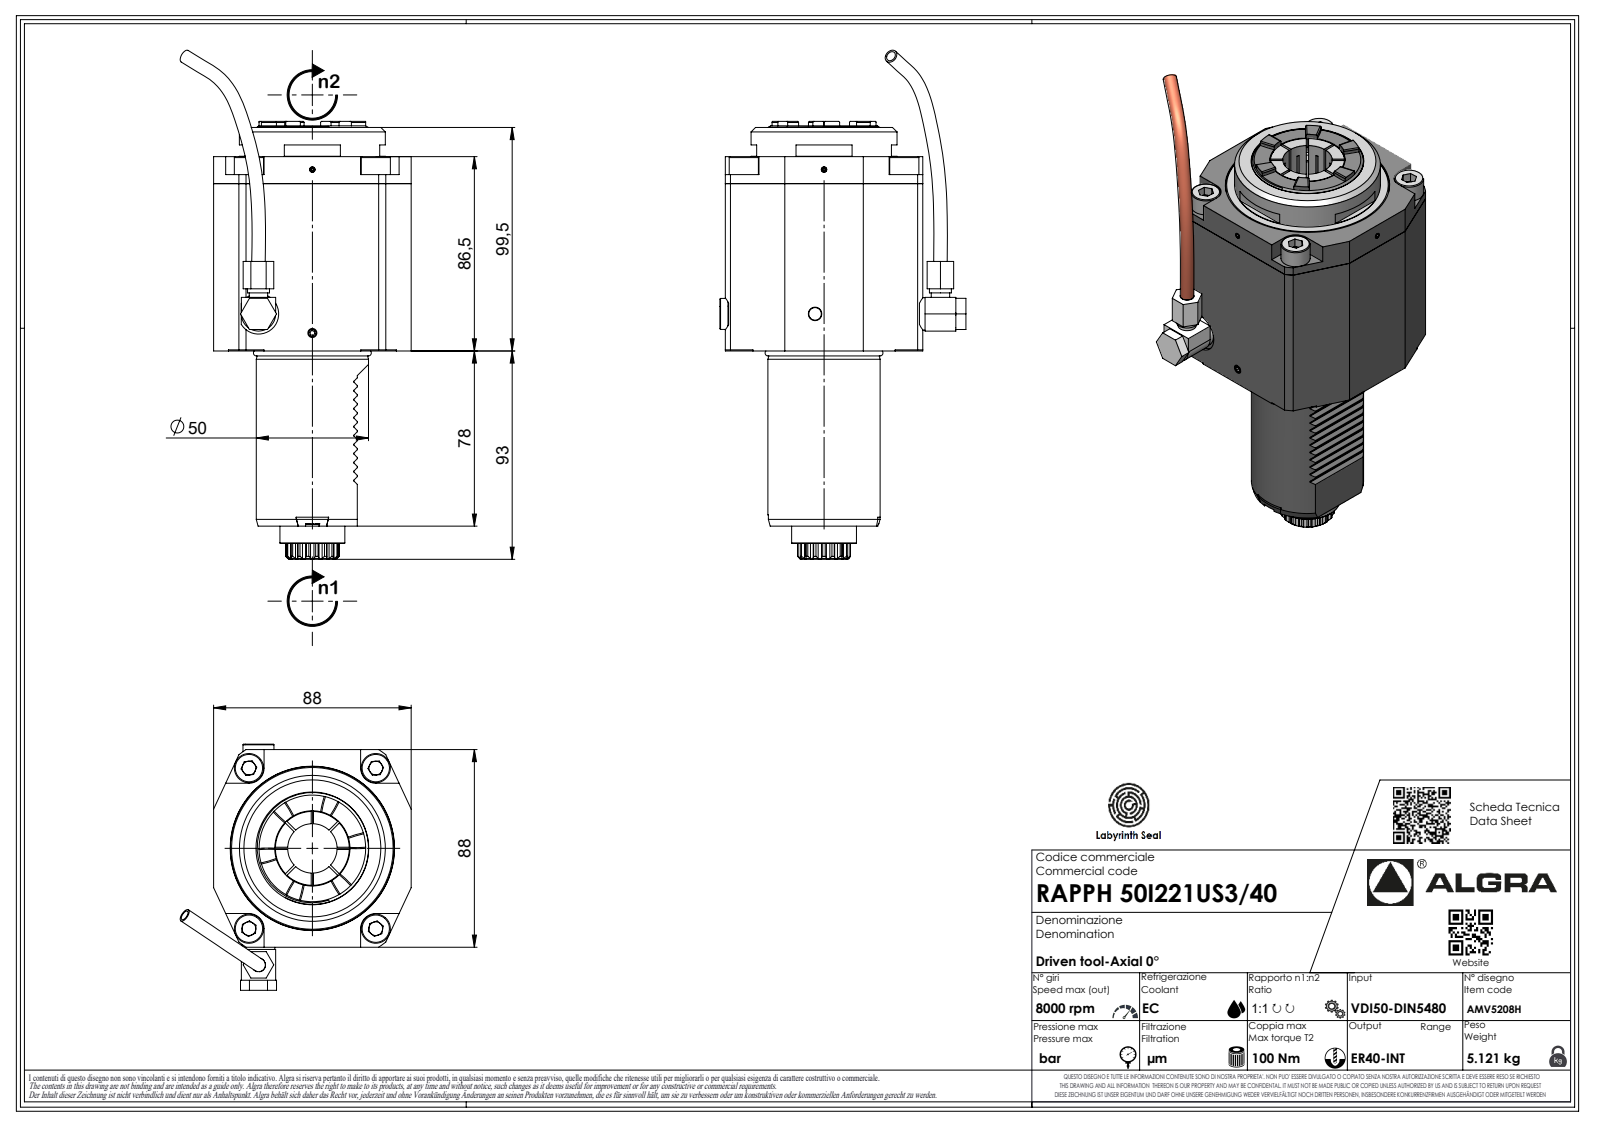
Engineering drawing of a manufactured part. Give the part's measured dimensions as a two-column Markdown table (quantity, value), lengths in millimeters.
| quantity | value |
| --- | --- |
| part name | RAPPH50I221US340 |
| STEP written by | SolidWorks 2023 (AUTOMOTIVE_DESIGN) |
| units | millimeters |
| bodies | 6 solids, 614 faces (348 planar, 120 cylindrical, 146 other) |
| overall size | 192.25 × 90.4 × 88 |
| volume | 807 235 mm³ |
| surface area | 59 175 mm² |
| round holes (diameter × count) | 2.1 × 1, 2.5 × 1, 31 × 1 |
| round bosses / shafts (diameter × count) | 2.3 × 2, 65 × 1, 57.24 × 1, 50 × 1, 28.9 × 1, 13.8 × 1, 6.37 × 1, 5.7 × 1 |
| partial cylindrical surfaces (radius × count) | 1.61 × 36, 0.3 × 12, 0.33 × 7, 0.52 × 7, 3.7 × 7, 0.21 × 1, 3 × 1, 11.88 × 1 |
| main face-to-face distances | 88, 96.2, 86.5, 99.5, 13, 2.83, 14.14, 78, 164.5, 177.5 |
| hole center spacings | 21 |
